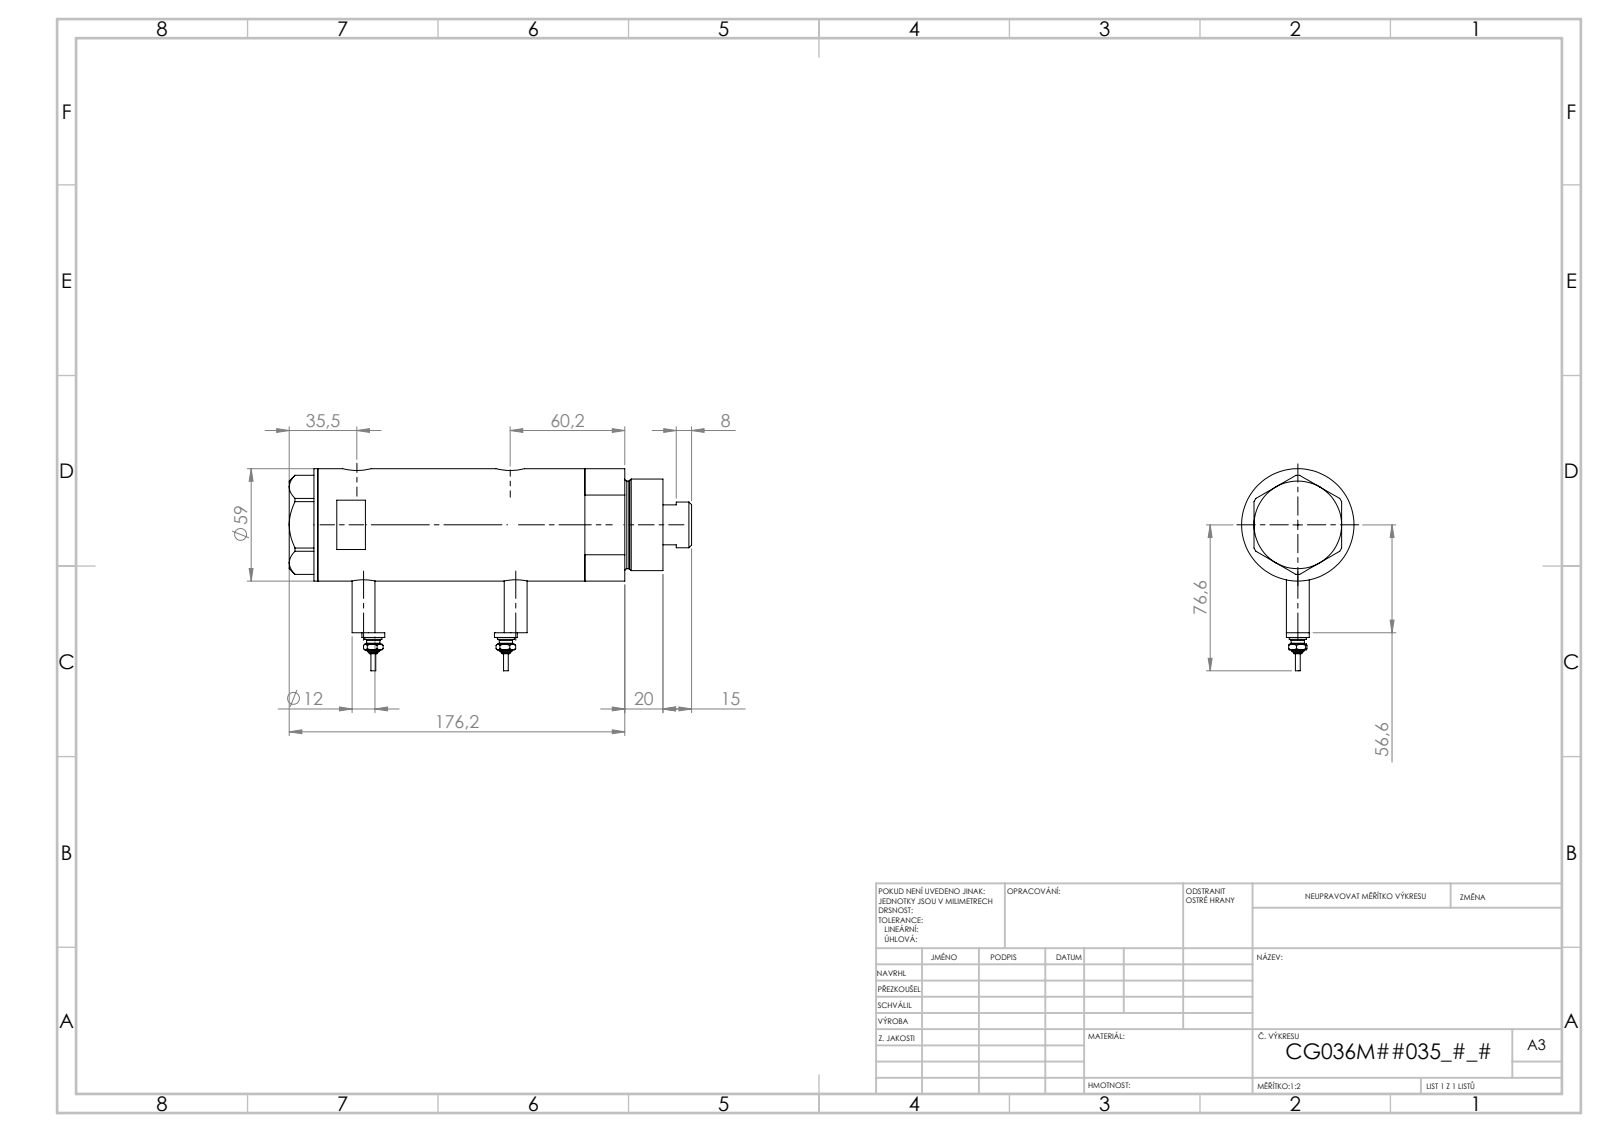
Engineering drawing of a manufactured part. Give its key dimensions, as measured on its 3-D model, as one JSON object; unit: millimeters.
{"part_name": "V270CG_BACK; V270CG_FRONT; V270CG_SWITCH; V270CG_MIDDLE (+1 more)", "step_written_by": "SolidWorks 2019 (CONFIG_CONTROL_DESIGN)", "units": "millimeters", "bodies": {"solids": 6, "faces": 232, "planar": 81, "cylindrical": 77, "other": 74}, "overall_size": [198.42, 91.3, 59], "volume_mm3": 451242, "surface_area_mm2": 97034, "round_holes": [[5, 2], [9.73, 2], [12.5, 2], [15, 2], [8.5, 1], [25, 1], [26.5, 1], [36, 1], [40, 1], [52, 1]], "round_bosses_or_shafts": [[12, 3], [9, 2], [7, 2], [4.34, 2], [2.4, 2], [59, 1], [48, 1], [46, 1]], "face_to_face_distances": [92.34, 23.5, 68.84, 15, 38.5, 107.34, 183.42, 168.42, 144.92, 76.08], "hole_center_spacings": [2.9, 3.5, 67.15, 70.05, 70.65, 73.55, 2.89, 2.91]}
